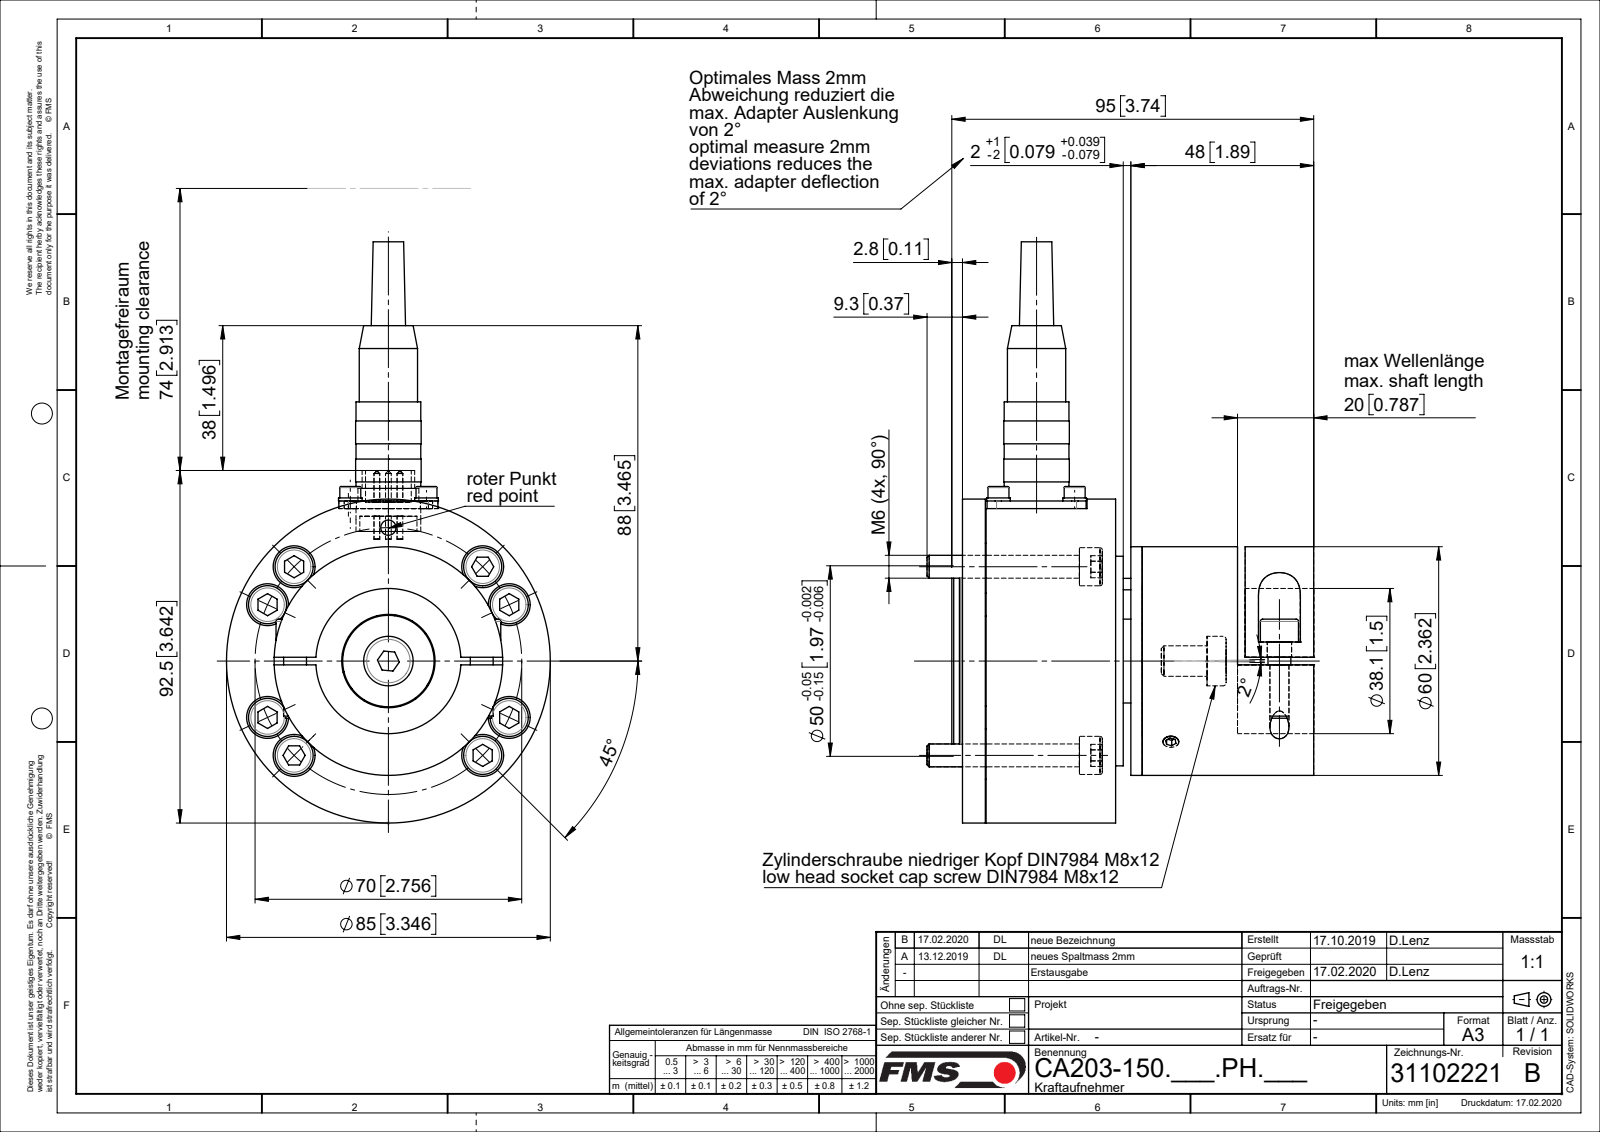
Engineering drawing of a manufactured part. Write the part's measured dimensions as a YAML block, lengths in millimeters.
part_name: "ZEICHNUNG10; C50331_DI150; C0709081; C0612056 (+8 more)"
step_written_by: "Mechanical Desktop 2009 (CONFIG_CONTROL_DESIGN)"
units: millimeters
bodies: {solids: 39, faces: 771, planar: 270, cylindrical: 349, other: 152}
overall_size: [152.5, 101, 85]
volume: 301231
surface_area: 117971
round_holes:
  - {diameter: 2.6, count: 8}
  - {diameter: 6.5, count: 8}
  - {diameter: 11, count: 8}
  - {diameter: 5.15, count: 6}
  - {diameter: 3.2, count: 4}
  - {diameter: 3.6, count: 4}
  - {diameter: 4, count: 4}
  - {diameter: 7, count: 4}
  - {diameter: 6.4, count: 2}
  - {diameter: 3, count: 1}
  - {diameter: 4.33, count: 1}
  - {diameter: 7.15, count: 1}
round_bosses_or_shafts:
  - {diameter: 6, count: 14}
  - {diameter: 10, count: 10}
  - {diameter: 3, count: 8}
  - {diameter: 1.5, count: 5}
  - {diameter: 6.2, count: 4}
  - {diameter: 5.5, count: 4}
  - {diameter: 5, count: 4}
  - {diameter: 85, count: 1}
partial_cylinders:
  - {radius: 4, count: 10}
  - {radius: 2.5, count: 4}
  - {radius: 5, count: 2}
  - {radius: 5.5, count: 2}
face_to_face_distances: [6, 11.5, 46.5, 2, 31.5, 1.5, 6.5, 3, 45, 40]
hole_center_spacings: [24.78, 25.2, 56.46, 20, 32.8, 35, 51.14, 28.28]
